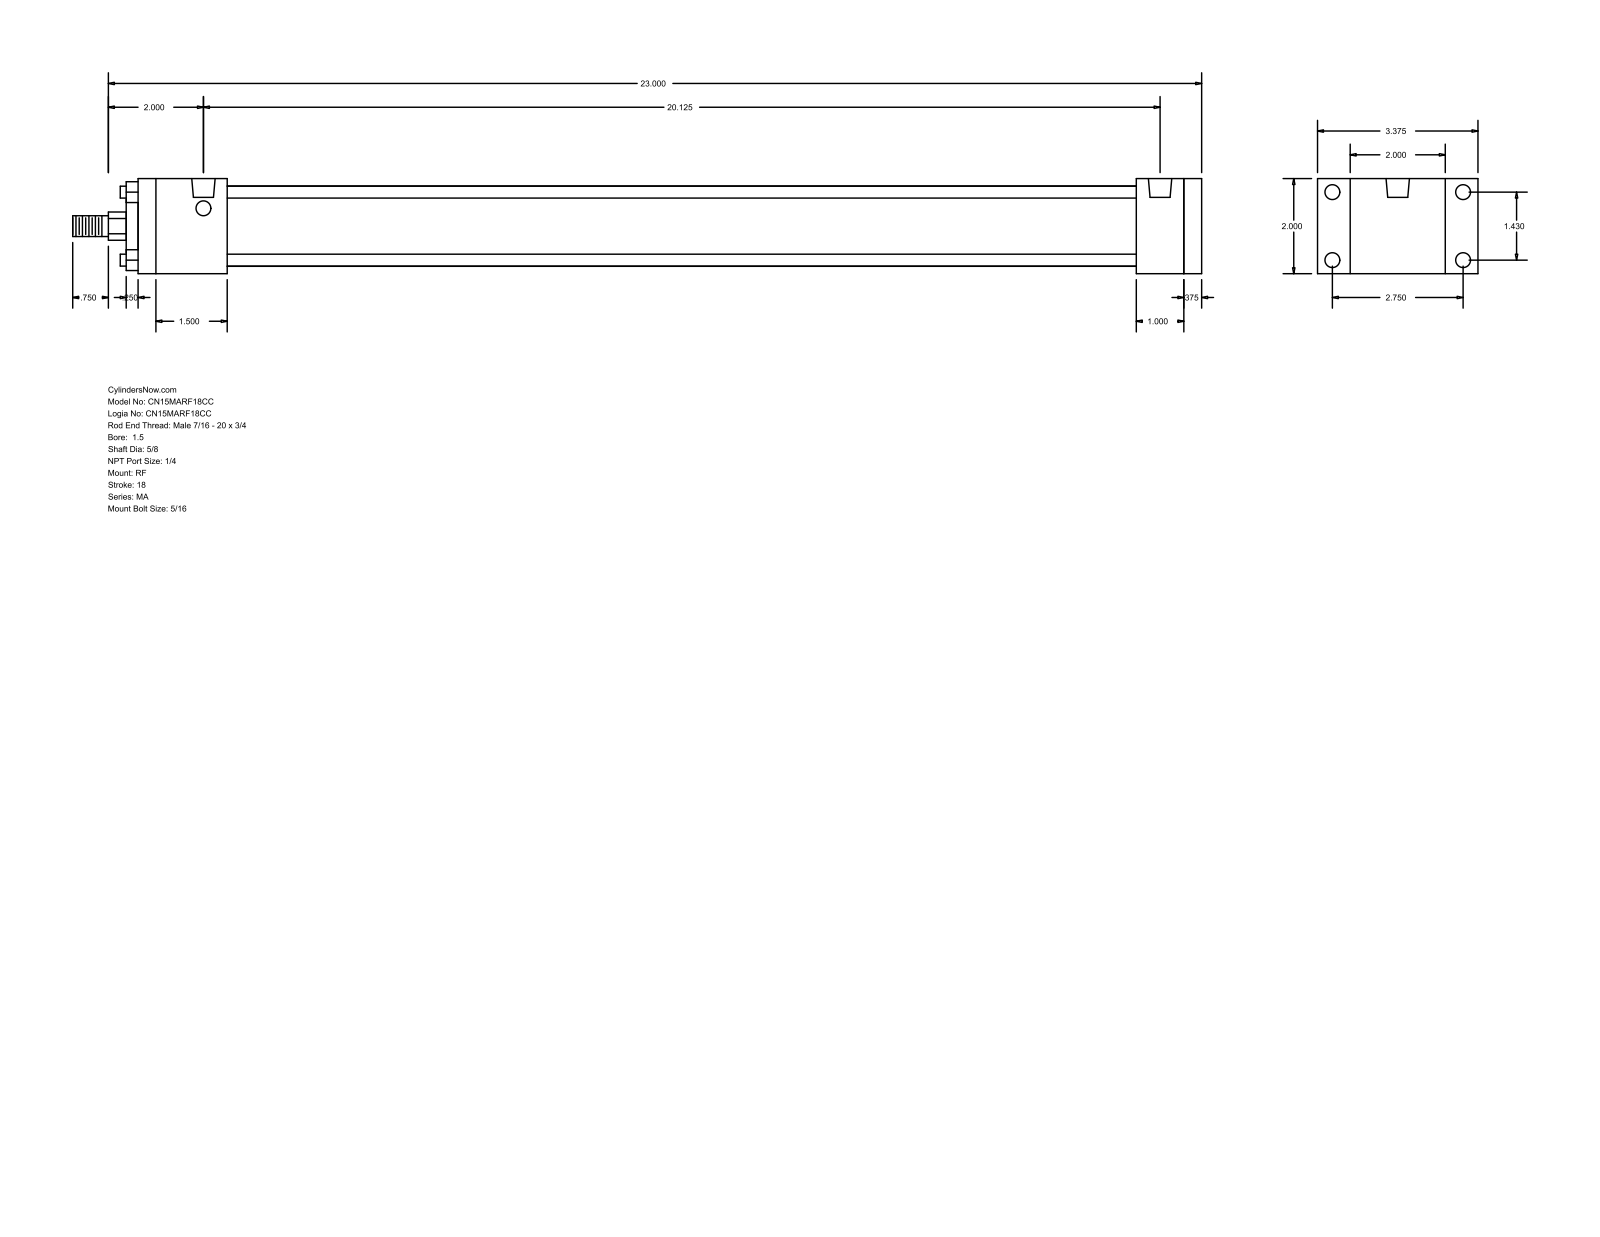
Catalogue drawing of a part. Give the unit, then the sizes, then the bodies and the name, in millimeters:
Units: millimetres
Overall size (bounding box): 603.25 × 85.72 × 50.8
Round holes (diameter × count): ⌀7.94 ×8, ⌀12.49 ×2
Round bosses / shafts (diameter × count): ⌀6.35 ×4, ⌀42.93 ×1, ⌀28.57 ×1, ⌀15.88 ×1, ⌀11.11 ×1
Partial cylindrical surfaces — rounded edges, fillets, slot ends (radius × count): R7.54 ×1
Main face-to-face distances: 50.8, 9.53, 568.32, 558.79, 25.4, 34.93, 533.39, 47.62, 485.77, 511.17
Hole centre spacings: 36.32, 69.84, 78.72, 511.18
Bodies: 0 solids, 92 faces (64 planar, 28 cylindrical, 0 other)
Part name (STEP PRODUCT): MA_RF__0150_0.625
STEP written by: GSSL Pune (CONFIG_CONTROL_DESIGN)
